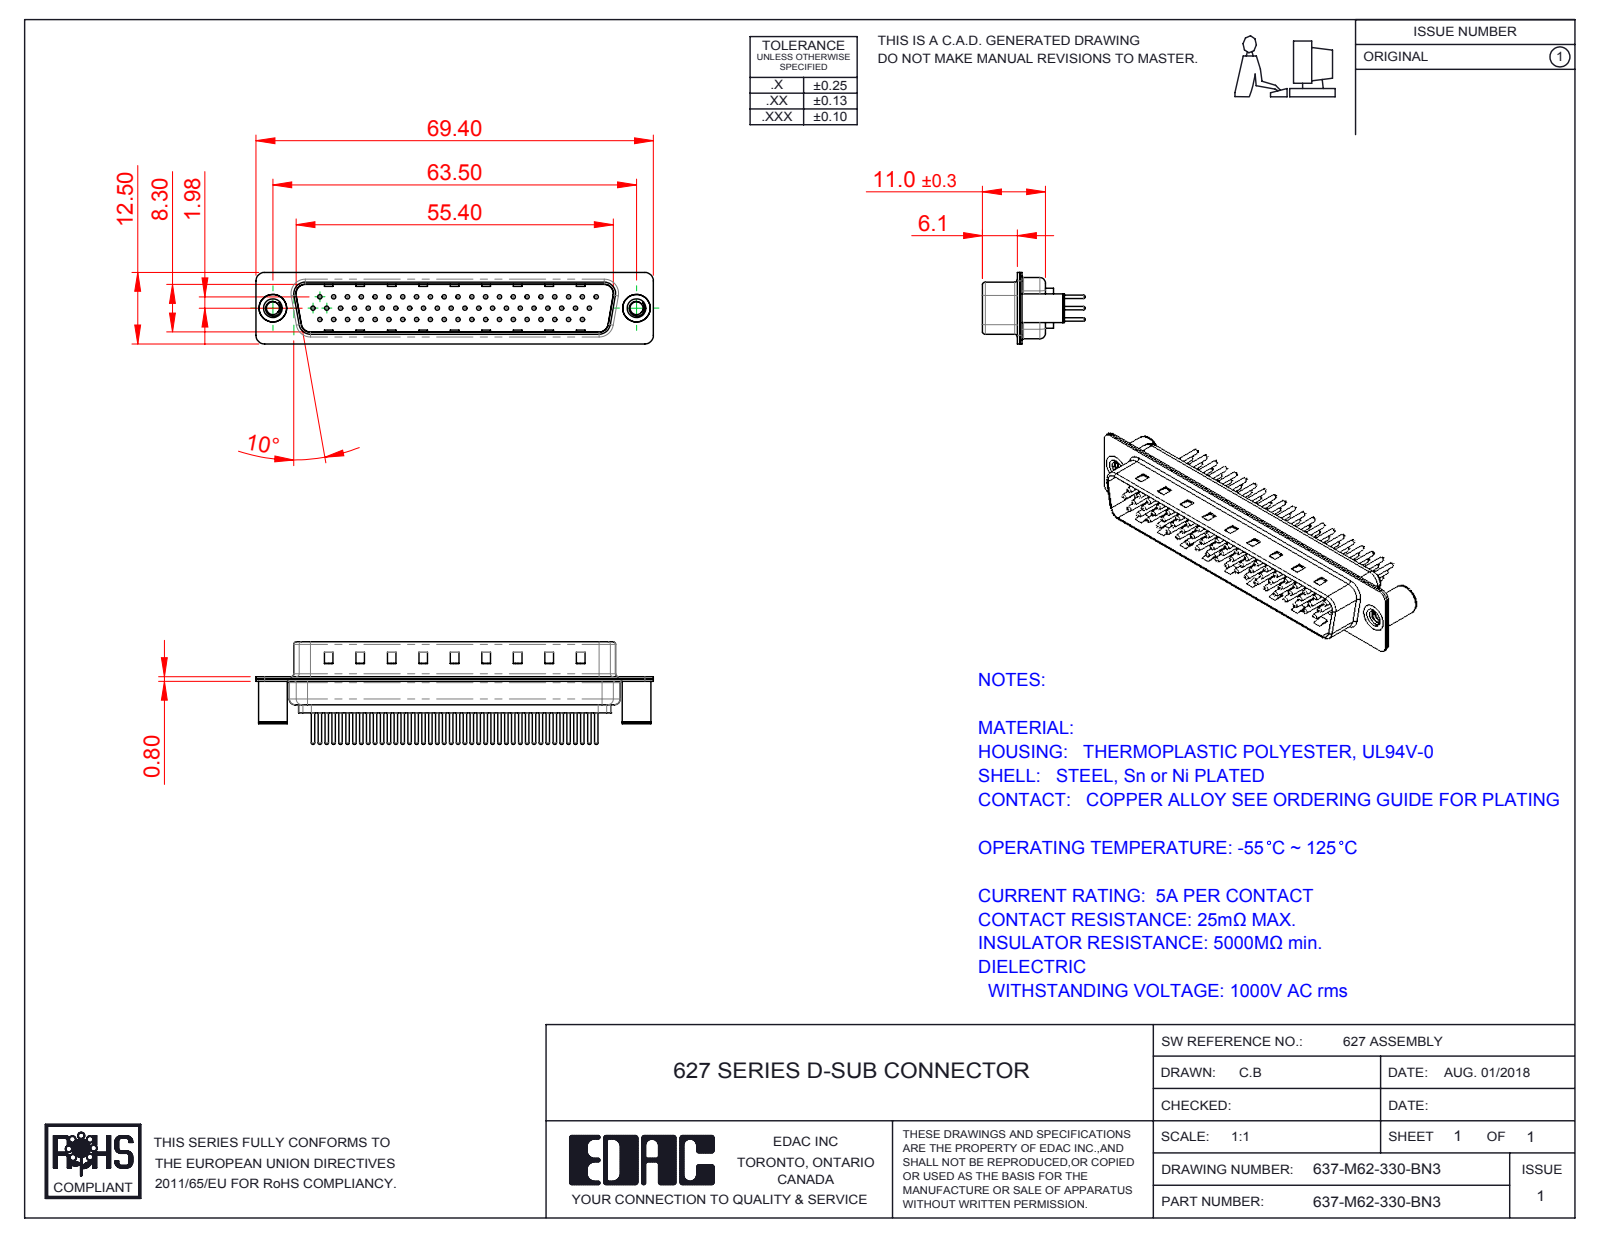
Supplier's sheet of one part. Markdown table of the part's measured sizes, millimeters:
| quantity | value |
| --- | --- |
| part name | 637M Contact Row 1_30; 637M Contact Row 3_30; 637M Shell Rear_62 Contacts; 637-M62-330-BN3 (+4 more) |
| STEP written by | SolidWorks 2016 (CONFIG_CONTROL_DESIGN) |
| units | millimeters |
| bodies | 67 solids, 2740 faces (637 planar, 1033 cylindrical, 1070 other) |
| overall size | 69.4 × 17.9 × 12.5 |
| volume | 4 040 mm³ |
| surface area | 11 672 mm² |
| round holes (diameter × count) | 0.75 × 62, 1.6 × 62, 2 × 62, 2.26 × 2, 3.26 × 2, 4 × 2, 4.8 × 2 |
| round bosses / shafts (diameter × count) | 1.5 × 62, 0.6 × 62, 5 × 2, 4.9 × 2 |
| partial cylindrical surfaces (radius × count) | 1.5 × 16, 2 × 12, 0.5 × 8, 1.6 × 8, 0.25 × 4, 0.6 × 4, 0.65 × 4, 0.9 × 4 |
| main face-to-face distances | 0.4, 0.8, 9.5, 9.1, 8.7, 9.9, 0.75, 0.35, 5.9, 1.2 |
| hole center spacings | 7.24, 2.32, 2.41, 4.13, 9.65, 4.83, 14.48, 11.04 |
